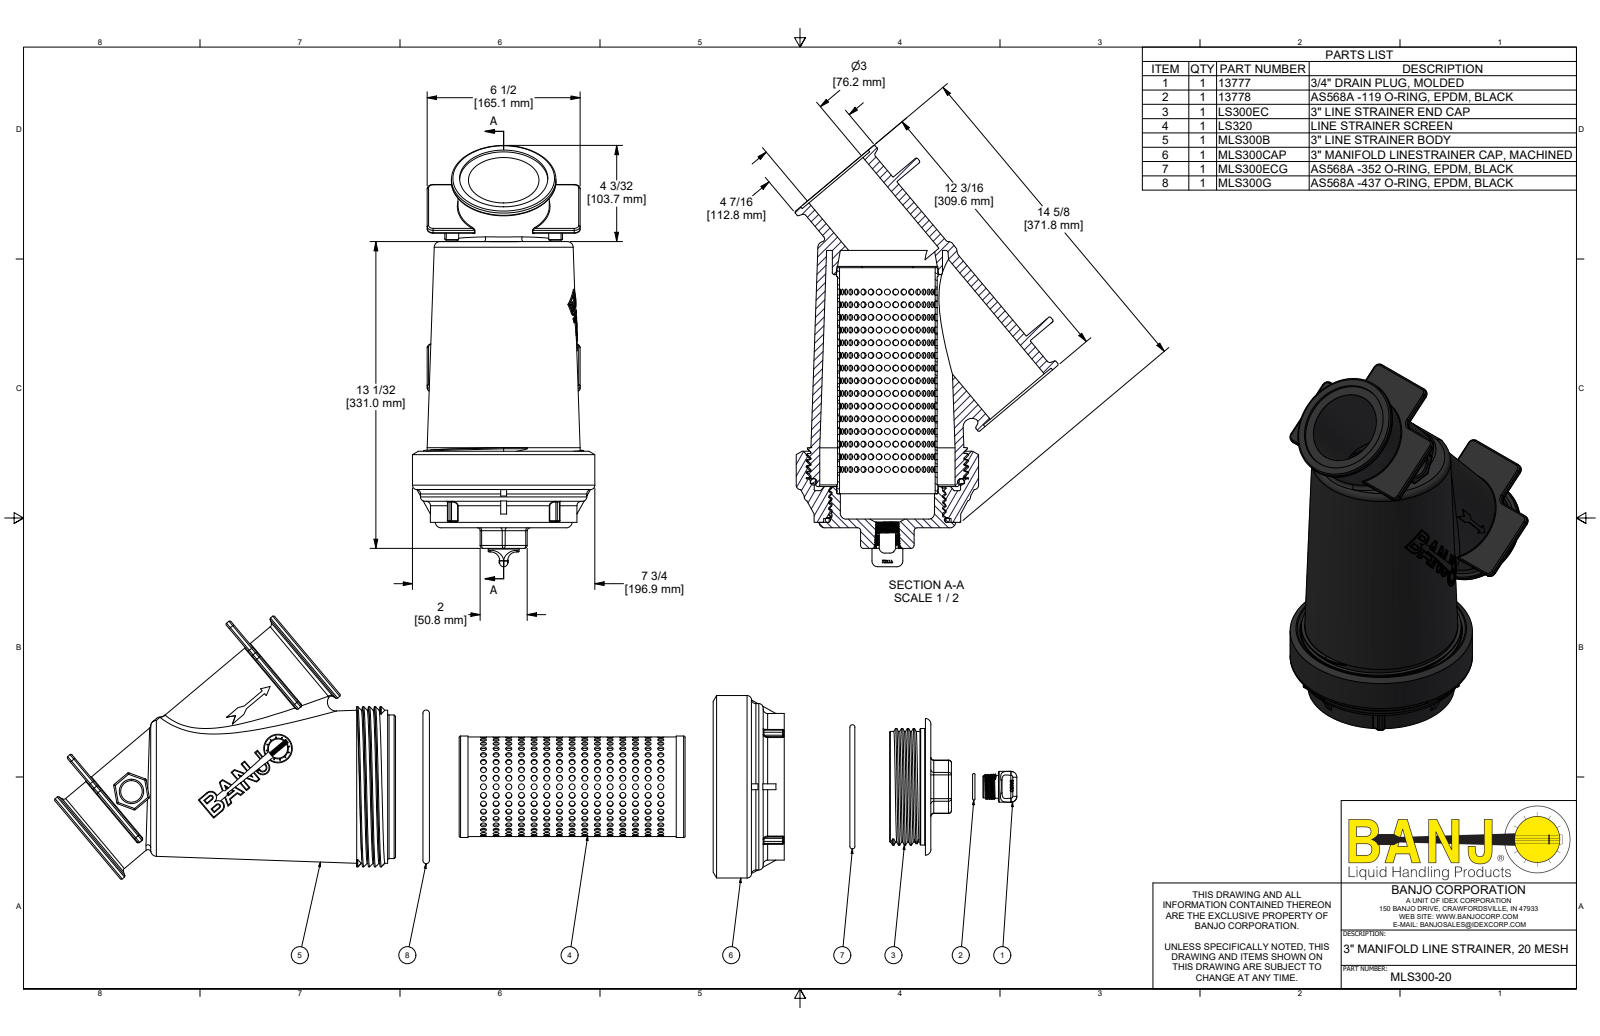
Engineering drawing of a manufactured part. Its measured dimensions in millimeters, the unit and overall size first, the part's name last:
Units: millimetres
Overall size (bounding box): 454.6 × 284.1 × 196.9
Round holes (diameter × count): ⌀6.4 ×495, ⌀95.3 ×2, ⌀17.8 ×1, ⌀20.8 ×1, ⌀23.1 ×1, ⌀29.3 ×1, ⌀76.2 ×1, ⌀101.6 ×1, ⌀103.2 ×1, ⌀109.7 ×1, ⌀109.7 ×1, ⌀120.1 ×1
Round bosses / shafts (diameter × count): ⌀112.8 ×2, ⌀98.6 ×2, ⌀196.9 ×1, ⌀179.6 ×1, ⌀172.7 ×1, ⌀165.1 ×1, ⌀158.2 ×1, ⌀154.9 ×1
Partial cylindrical surfaces — rounded edges, fillets, slot ends (radius × count): R1.5 ×46, R0.8 ×28, R3.2 ×18, R6.4 ×17, R0.5 ×8, R2.3 ×8, R0.4 ×6, R1.8 ×2
Main face-to-face distances: 6.4, 223.9, 5.8, 217.6, 230.3, 43.5, 37.1, 261, 267.4, 9.4
Hole centre spacings: 27.4, 13.7, 41, 54.7, 68.4, 95.7, 13.7, 82
Volume: 3 140 000 mm³ · Surface area: 818 700 mm²
Bodies: 8 solids, 1772 faces (478 planar, 824 cylindrical, 470 other)
Part name (STEP PRODUCT): MLS300-20; MLS300B; LS300EC; LS300ECX (+7 more)
STEP written by: Autodesk Inventor 2022 (AUTOMOTIVE_DESIGN)
